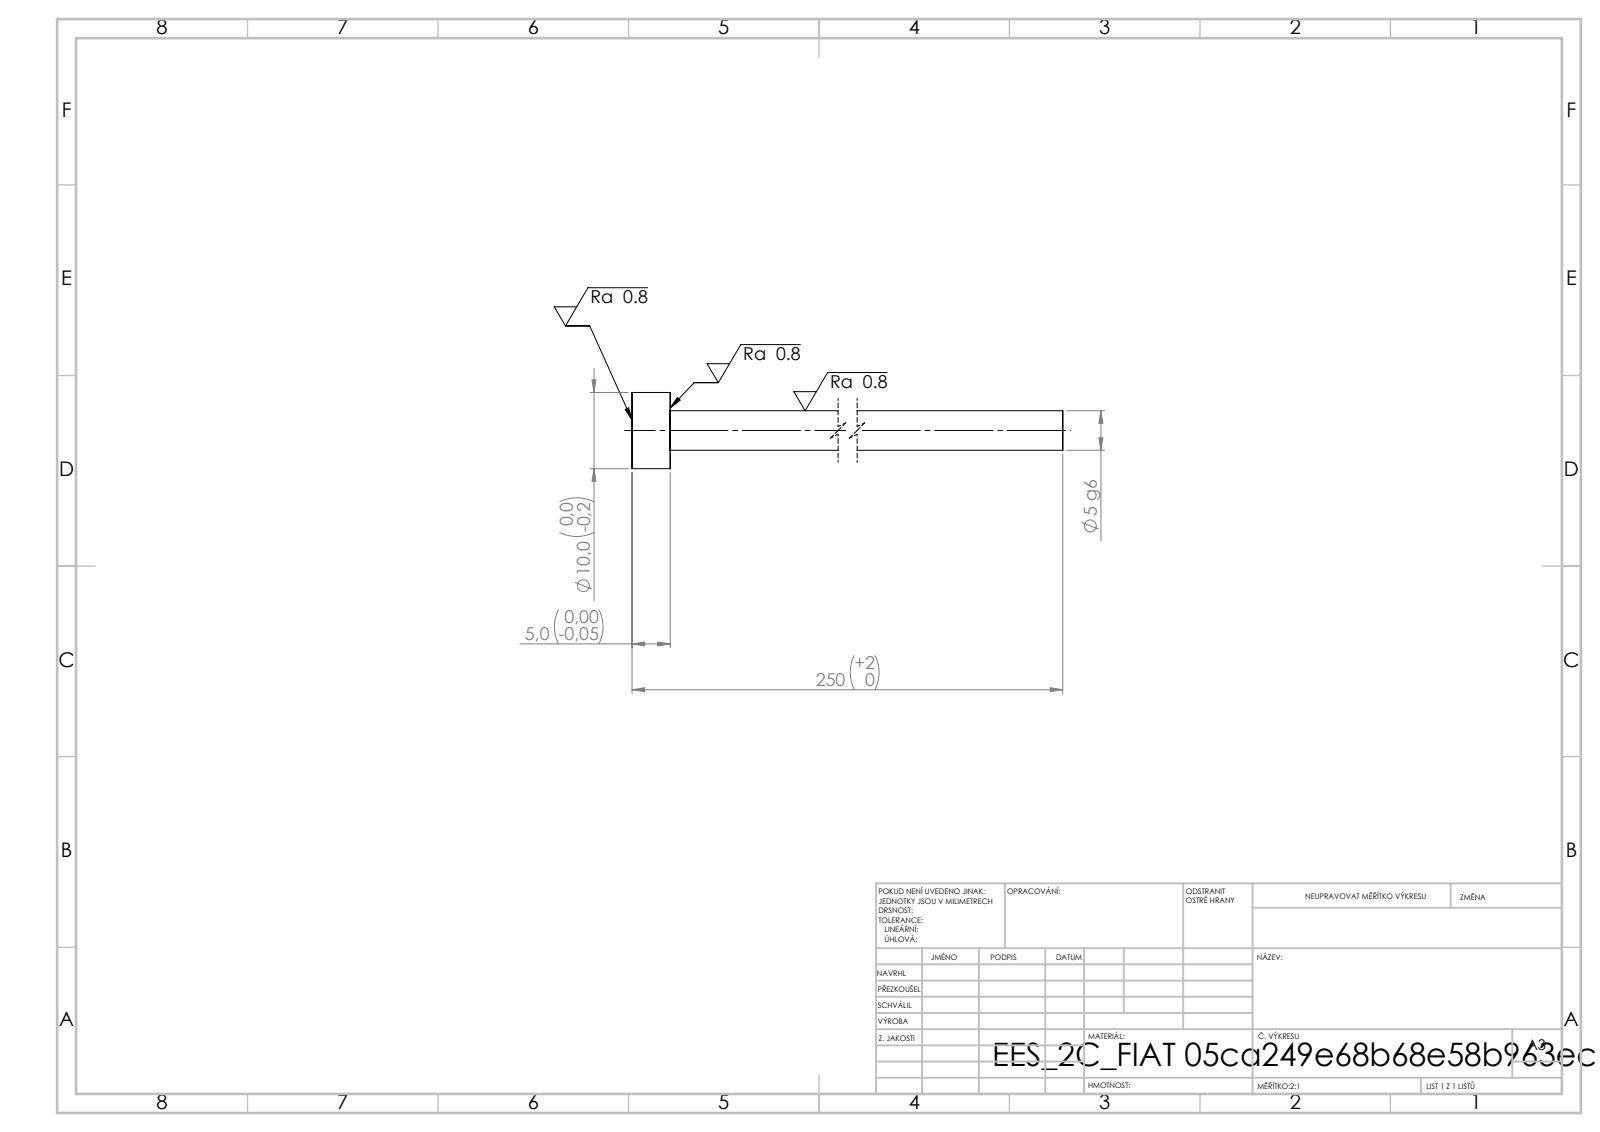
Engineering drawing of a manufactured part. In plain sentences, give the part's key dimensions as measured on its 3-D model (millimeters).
Its 3-D file was written by "SolidWorks 2019 (CONFIG_CONTROL_DESIGN)". It is 1 solid with 7 faces: 3 planar, 4 cylindrical and 0 other. Overall it measures 250 by 10 by 10 millimeters. Its volume is 5 596 cubic millimeters and its surface area 4 317 square millimeters. Round bosses or shafts: 1 of diameter 10, 1 of diameter 5.2. The main face-to-face distances are 5, 250, 245.
